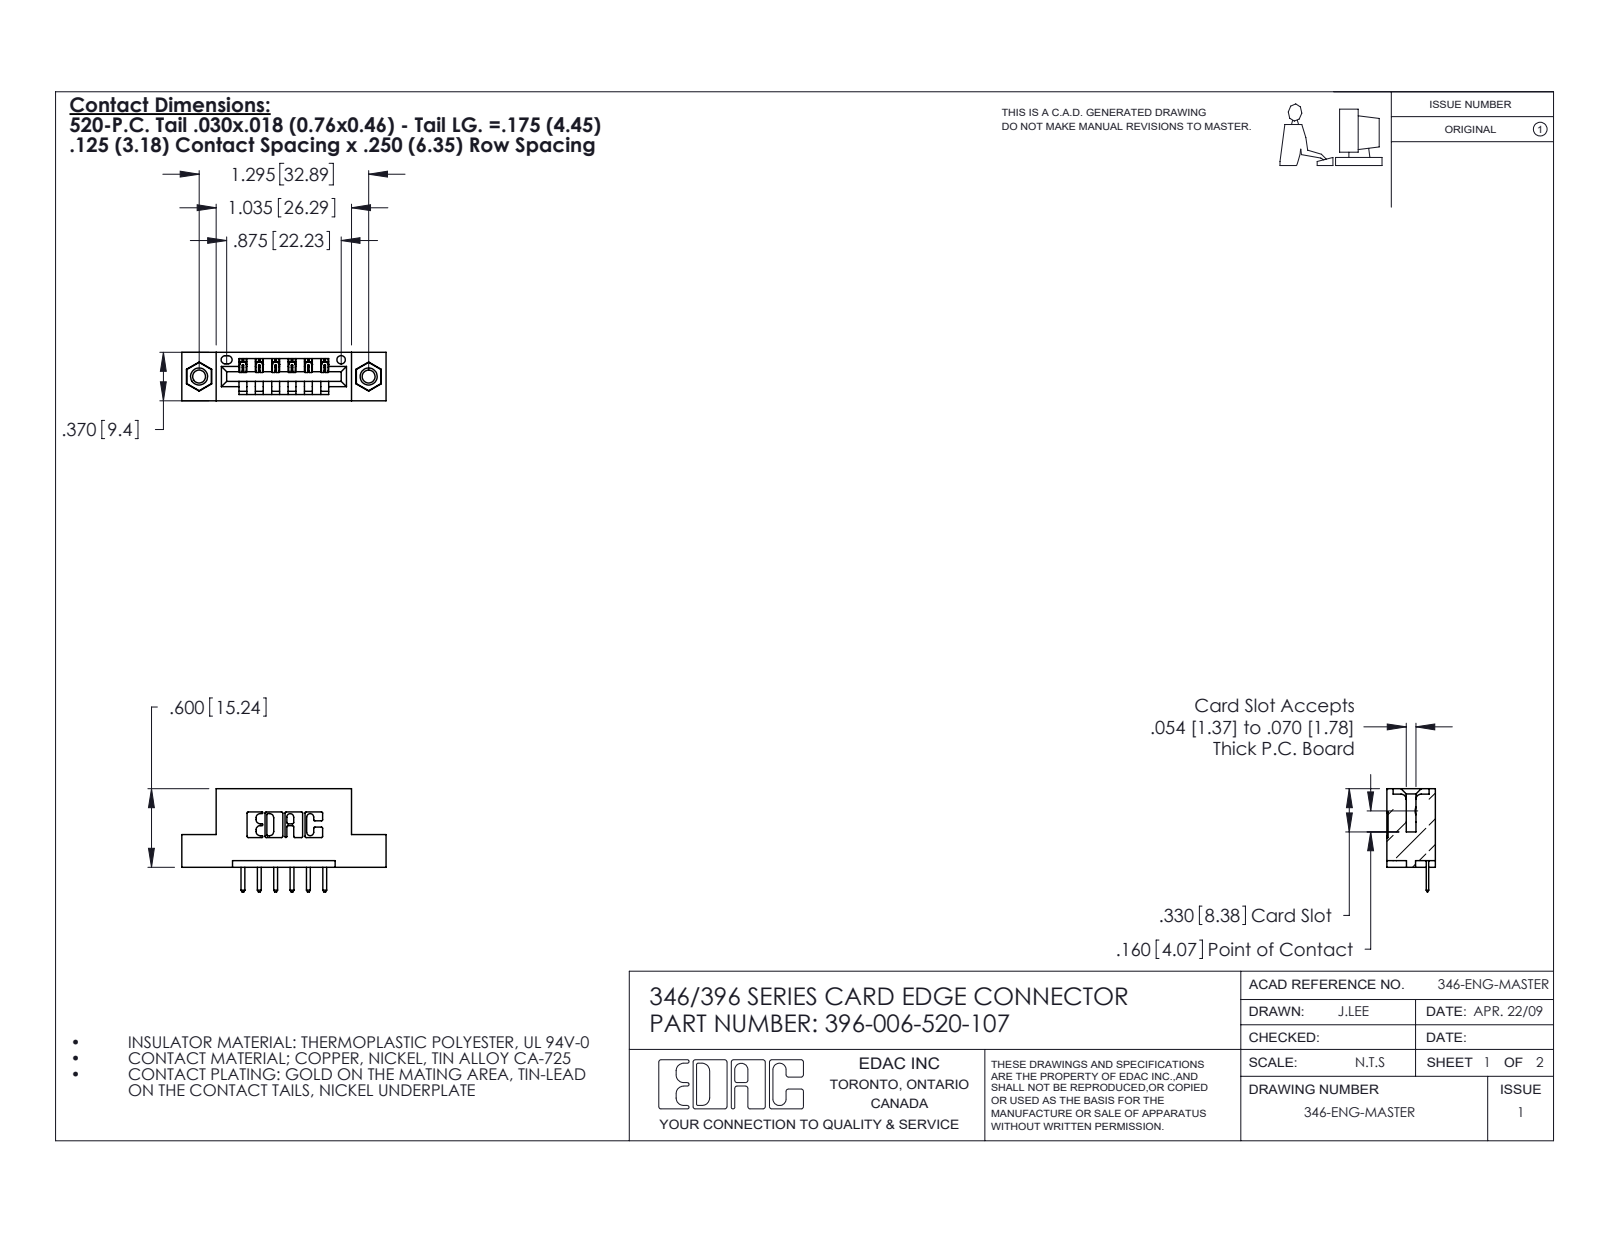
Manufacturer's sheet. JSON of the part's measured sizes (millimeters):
{"part_name": "396-006-520-107; 346 Part_Flush Mounting Lugs - 0.156 Dia-TI; 345-250-001_345-250-005-103; 345-292-001_345-293-120", "step_written_by": "SolidWorks 2020 (CONFIG_CONTROL_DESIGN)", "units": "millimeters", "bodies": {"solids": 9, "faces": 554, "planar": 360, "cylindrical": 178, "other": 16}, "overall_size": [39.6, 20, 9.4], "volume_mm3": 3510, "surface_area_mm2": 3981, "round_holes": [[2.5, 2], [3.2, 2], [4, 2], [1.6, 1]], "round_bosses_or_shafts": [[3.9, 2]], "partial_cylinders_radius": [[0.3, 22], [0.3, 14], [0.2, 12], [0.2, 6], [0.8, 6], [0.7, 3], [0.8, 2], [1, 2]], "face_to_face_distances": [6.4, 9.4, 1.2, 8.2, 3.8, 5.6, 2.5, 4.4, 3.2, 3.2], "hole_center_spacings": [6.2, 27.7, 32.9]}
